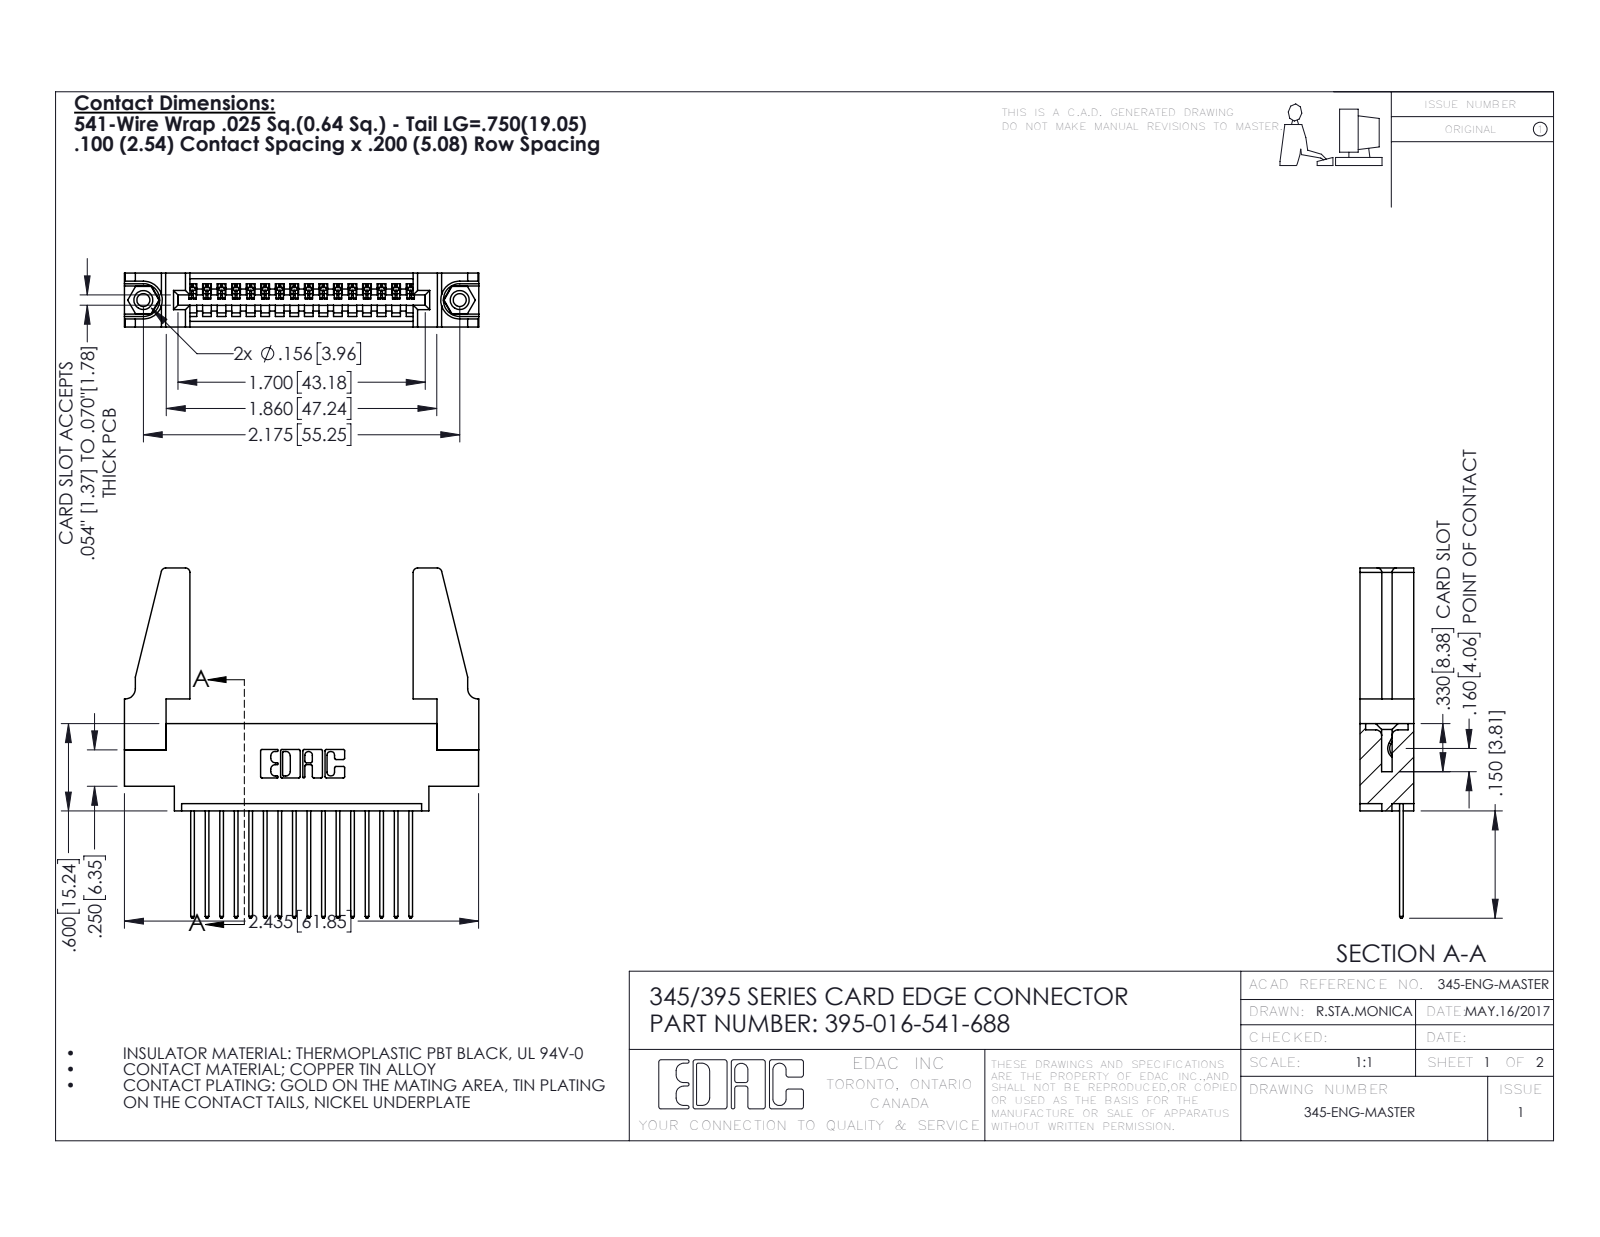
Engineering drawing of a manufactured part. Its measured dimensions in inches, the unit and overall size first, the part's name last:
Units: inches
Overall size (bounding box): 2.436 × 2.407 × 0.37
Round holes (diameter × count): ⌀0.089 ×2, ⌀0.125 ×2, ⌀0.156 ×2, ⌀0.064 ×1
Round bosses / shafts (diameter × count): ⌀0.155 ×2
Partial cylindrical surfaces — rounded edges, fillets, slot ends (radius × count): R0.006 ×32, R0.01 ×32, R0.01 ×22, R0.03 ×8, R0.007 ×6, R0.031 ×6, R0.026 ×3, R0.031 ×2
Main face-to-face distances: 0.37, 0.072, 0.298, 0.098, 0.272, 0.025, 0.2, 0.225, 0.148, 0.15
Hole centre spacings: 0.27, 1.942, 2.175
Volume: 0.54 in³ · Surface area: 16.52 in²
Bodies: 21 solids, 1182 faces (796 planar, 370 cylindrical, 16 other)
Part name (STEP PRODUCT): 345 Part_0.170 Offset - 0.156 Dia-TH; 395-016-541-688; 345-220-078_345-220-088; 345-292-001_345-293-141 (+1 more)
STEP written by: SolidWorks 2016 (CONFIG_CONTROL_DESIGN)
